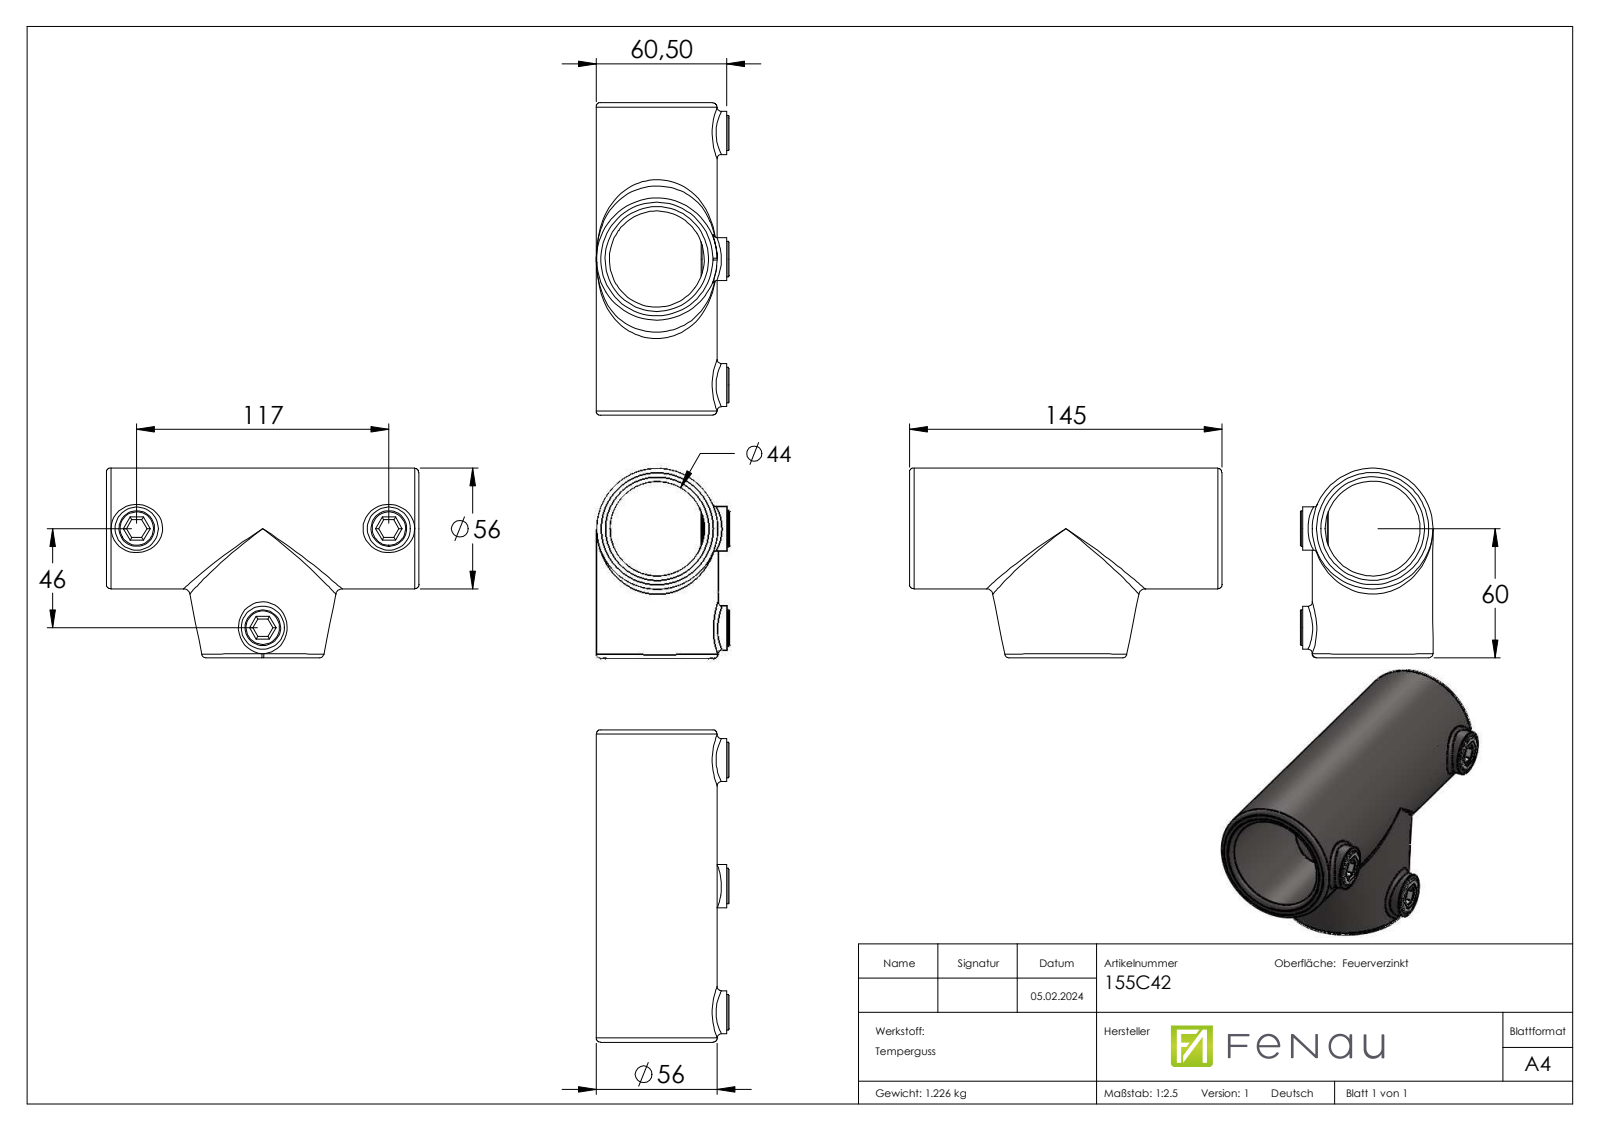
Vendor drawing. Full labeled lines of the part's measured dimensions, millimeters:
Part name (STEP PRODUCT): 155-C42 Teil1_155-C42 Teil1; 155-C42; 155-C42 Teil2_155-C42 Teil2
STEP written by: SolidWorks 2018 (CONFIG_CONTROL_DESIGN)
Units: millimetres
Bodies: 4 solids, 97 faces (30 planar, 47 cylindrical, 20 other)
Overall size (bounding box): 145 × 88 × 61.5
Volume: 168 534 mm³ · Surface area: 61 973 mm²
Round holes (diameter × count): ⌀15.25 ×3, ⌀44 ×1
Round bosses / shafts (diameter × count): ⌀20 ×3, ⌀16.5 ×3, ⌀56 ×1
Partial cylindrical surfaces — rounded edges, fillets, slot ends (radius × count): R2 ×32
Main face-to-face distances: 8.1, 145, 12, 13, 1, 27.66, 101.32, 73.66, 55.95, 64.05
Hole centre spacings: 74.42, 117
